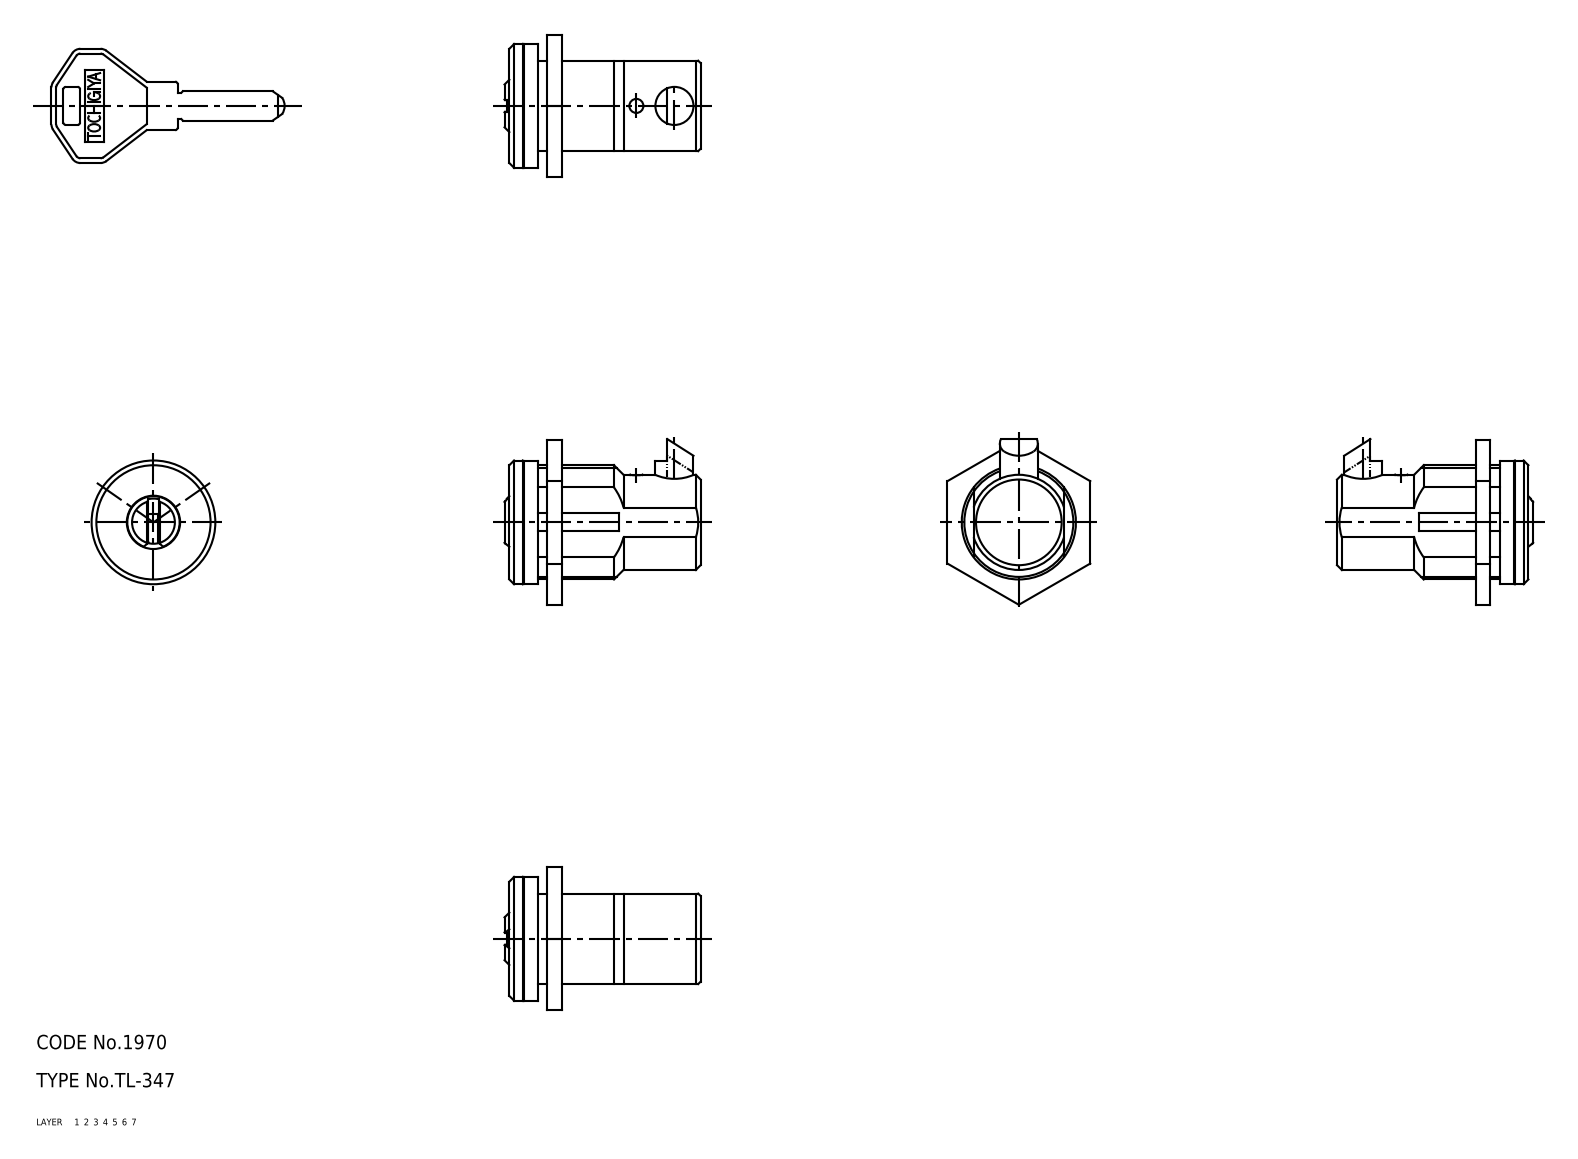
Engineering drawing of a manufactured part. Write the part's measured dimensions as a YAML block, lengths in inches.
part_name: "spacer; nut; lock; latch (+2 more)"
step_written_by: "CADfix (AUTOMOTIVE_DESIGN)"
units: inches
bodies: {solids: 5, faces: 125, planar: 0, cylindrical: 0, other: 125}
overall_size: [4.783, 1.371, 1.181]
volume: 1.035
surface_area: 12.91
